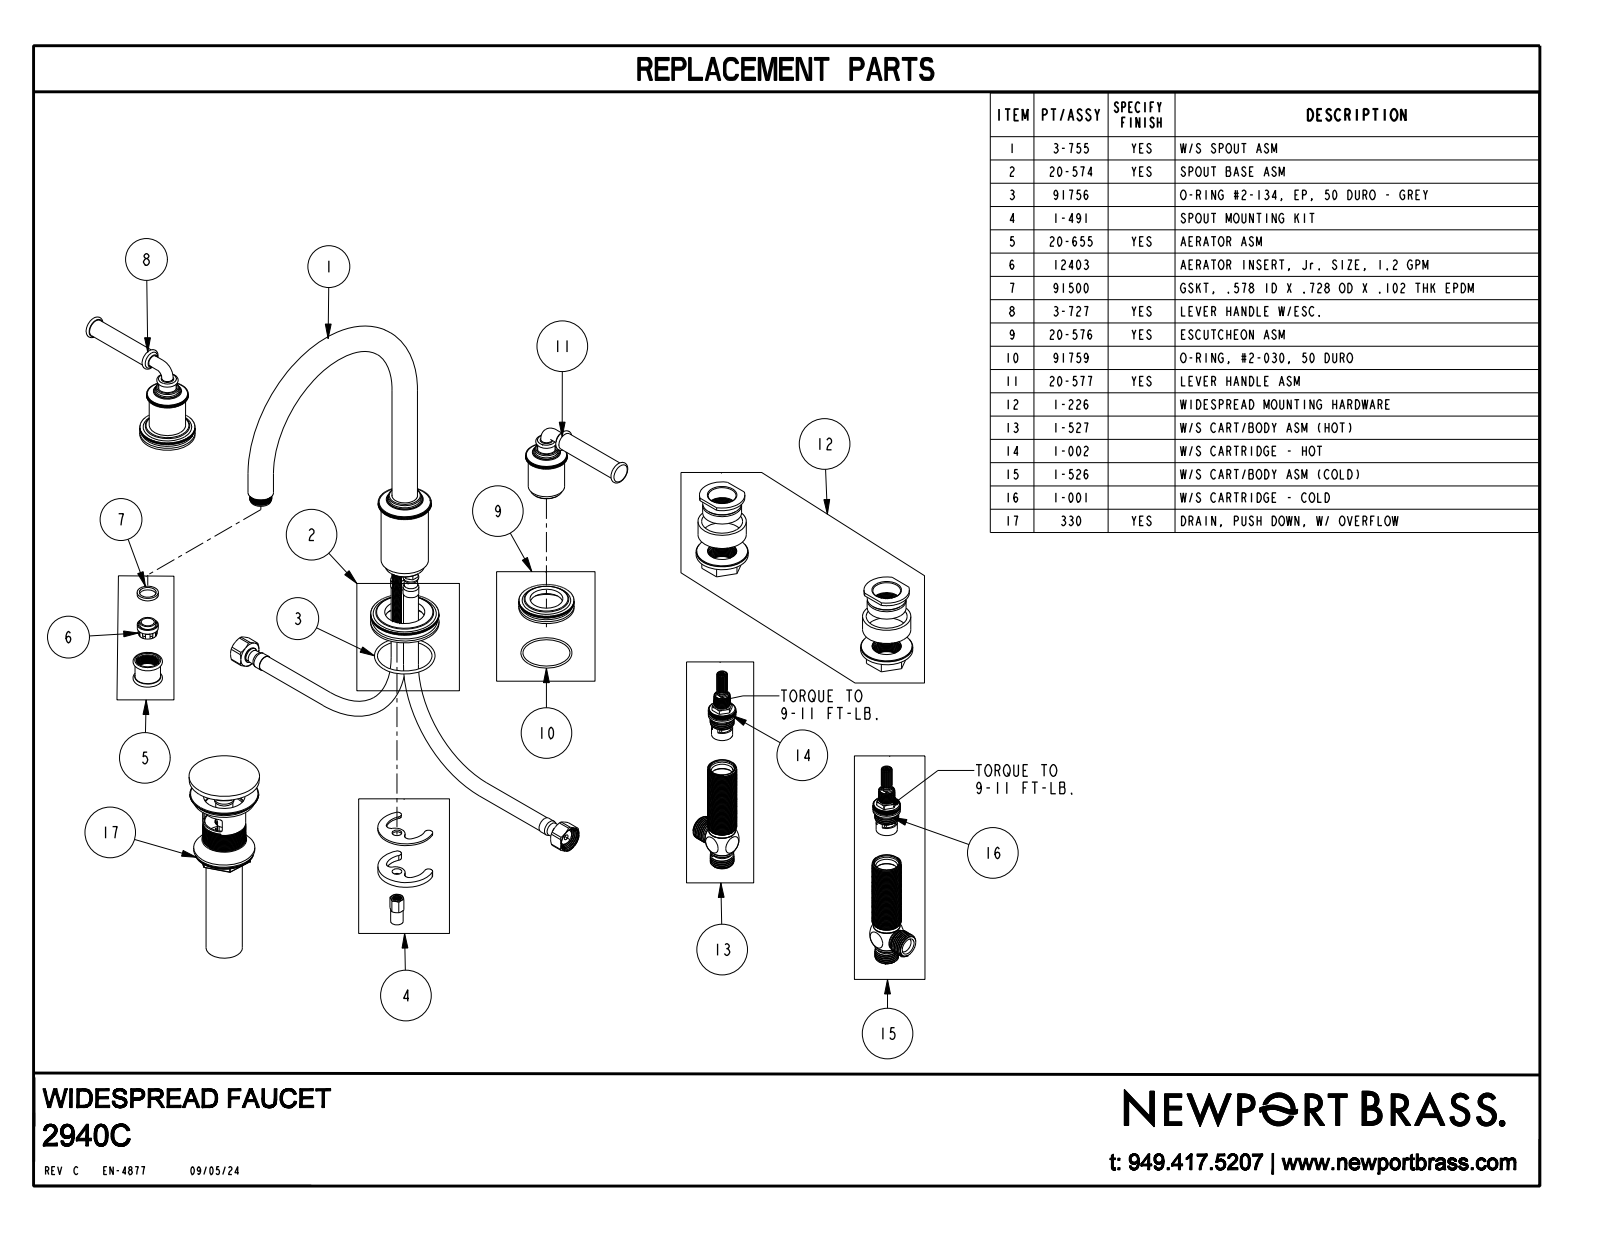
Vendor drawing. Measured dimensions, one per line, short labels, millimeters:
name: 2940C_SW0001
written by: CREO PARAMETRIC BY PTC INC, 2018400 (CONFIG_CONTROL_DESIGN)
unit: mm
bodies: 3 solids, 2237 faces (1420 planar, 741 cylindrical, 76 other)
size: 386.3 × 293.7 × 223.7
volume: 417 500 mm³; area: 77 940 mm²
bosses: 3× ⌀9.9, 2× ⌀48.3, 2× ⌀45.7, 2× ⌀31.8, 2× ⌀30.5, 2× ⌀22.2, 2× ⌀20.3, 2× ⌀15.1
rounds: 2× R18.2, 1× R23.2
face distances: 2.3, 1.8, 4.1, 2, 7.9, 11.9, 9.7, 3.8, 30.7, 31.2
